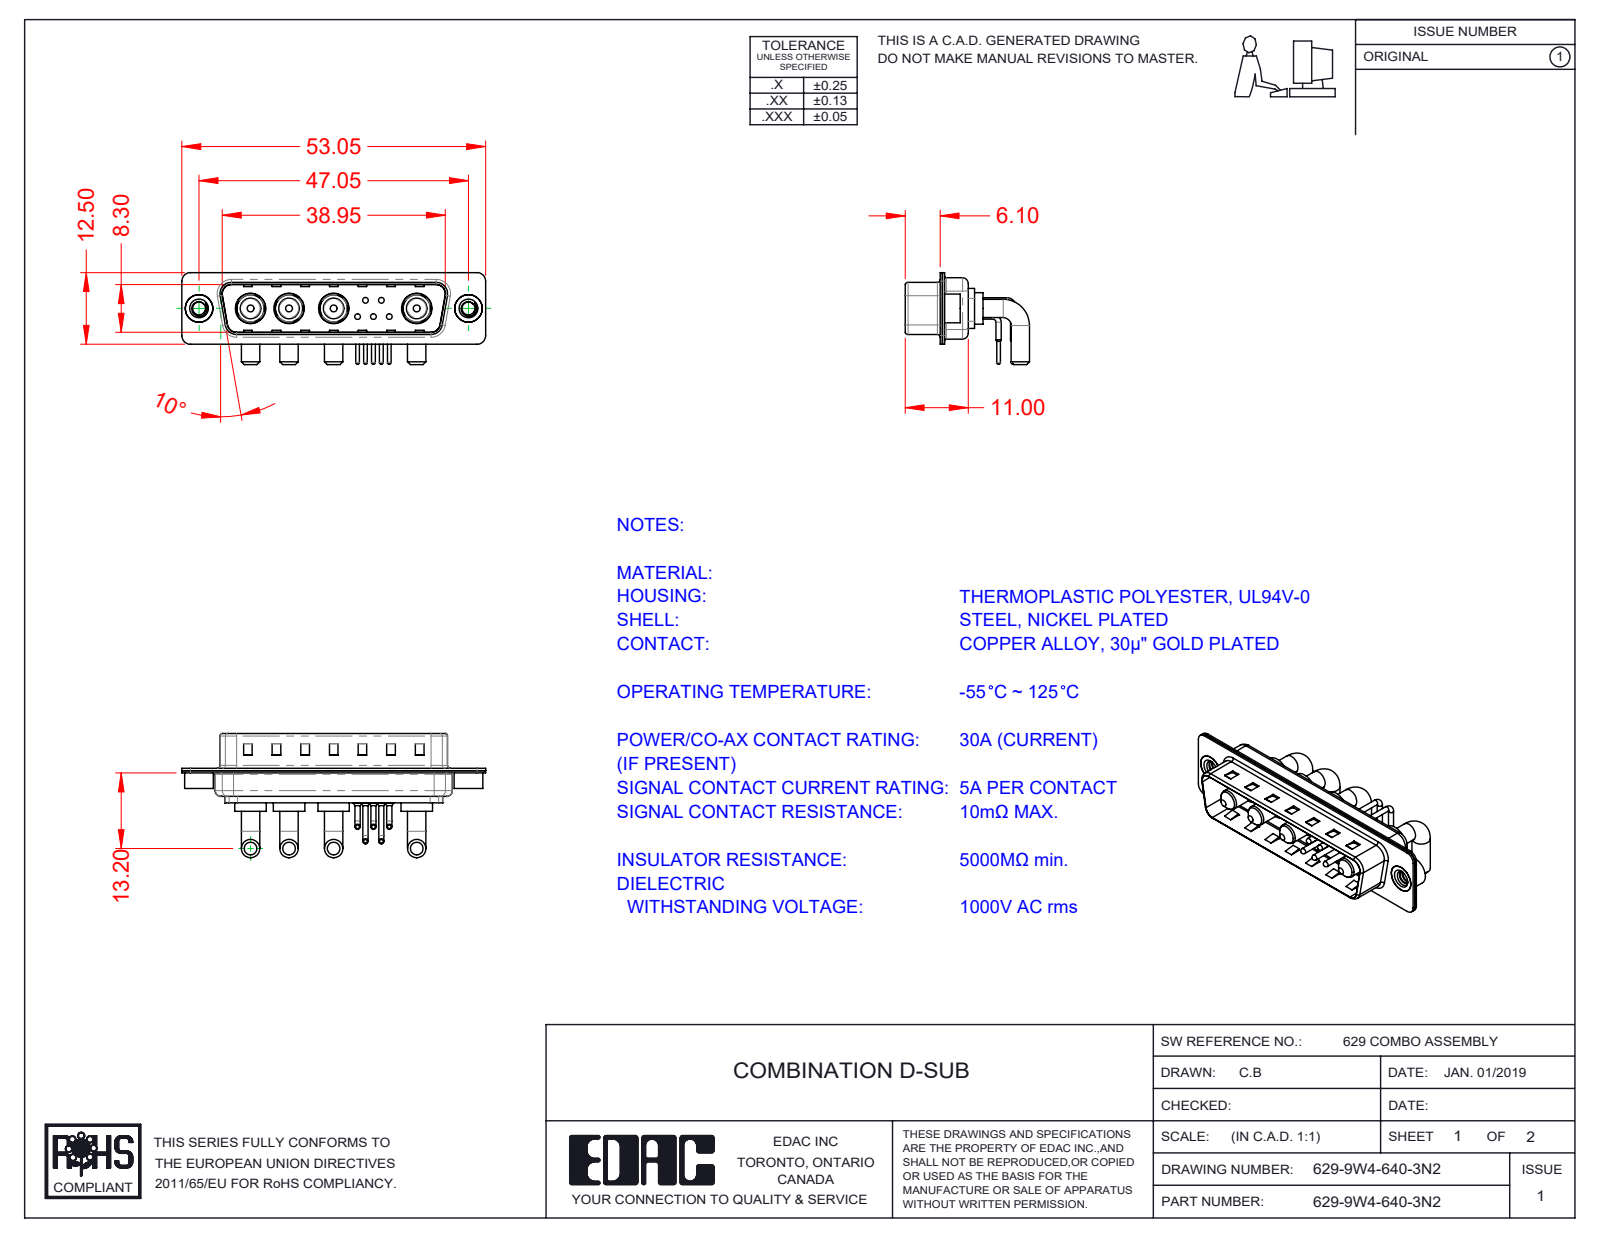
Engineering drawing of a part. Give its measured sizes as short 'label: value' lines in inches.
name: 629Combo Housing_9W4; Power Pin_30A RA; 629Combo Threaded Rivet_2; 629-9W4-640-3N2 (+4 more)
written by: SolidWorks 2020 (CONFIG_CONTROL_DESIGN)
unit: in
bodies: 18 solids, 1098 faces (531 planar, 401 cylindrical, 166 other)
size: 2.089 × 0.854 × 0.632
volume: 0.209 in³; area: 11.35 in²
holes: 5× ⌀0.03, 5× ⌀0.063, 5× ⌀0.079, 4× ⌀0.191, 4× ⌀0.209, 2× ⌀0.089, 2× ⌀0.157, 2× ⌀0.189
bosses: 10× ⌀0.035, 8× ⌀0.126, 5× ⌀0.059, 5× ⌀0.039, 5× ⌀0.026, 4× ⌀0.217, 4× ⌀0.205, 4× ⌀0.187
rounds: 16× R0.059, 12× R0.079, 8× R0.02, 8× R0.063, 5× R0.04, 4× R0.01, 4× R0.024, 4× R0.026
face distances: 0.016, 0.031, 0.374, 0.358, 0.343, 0.39, 0.03, 0.047, 0.22, 0.014
hole spacings: 0.124, 0.109, 0.198, 0.571, 0.109, 0.173, 0.174, 0.197
